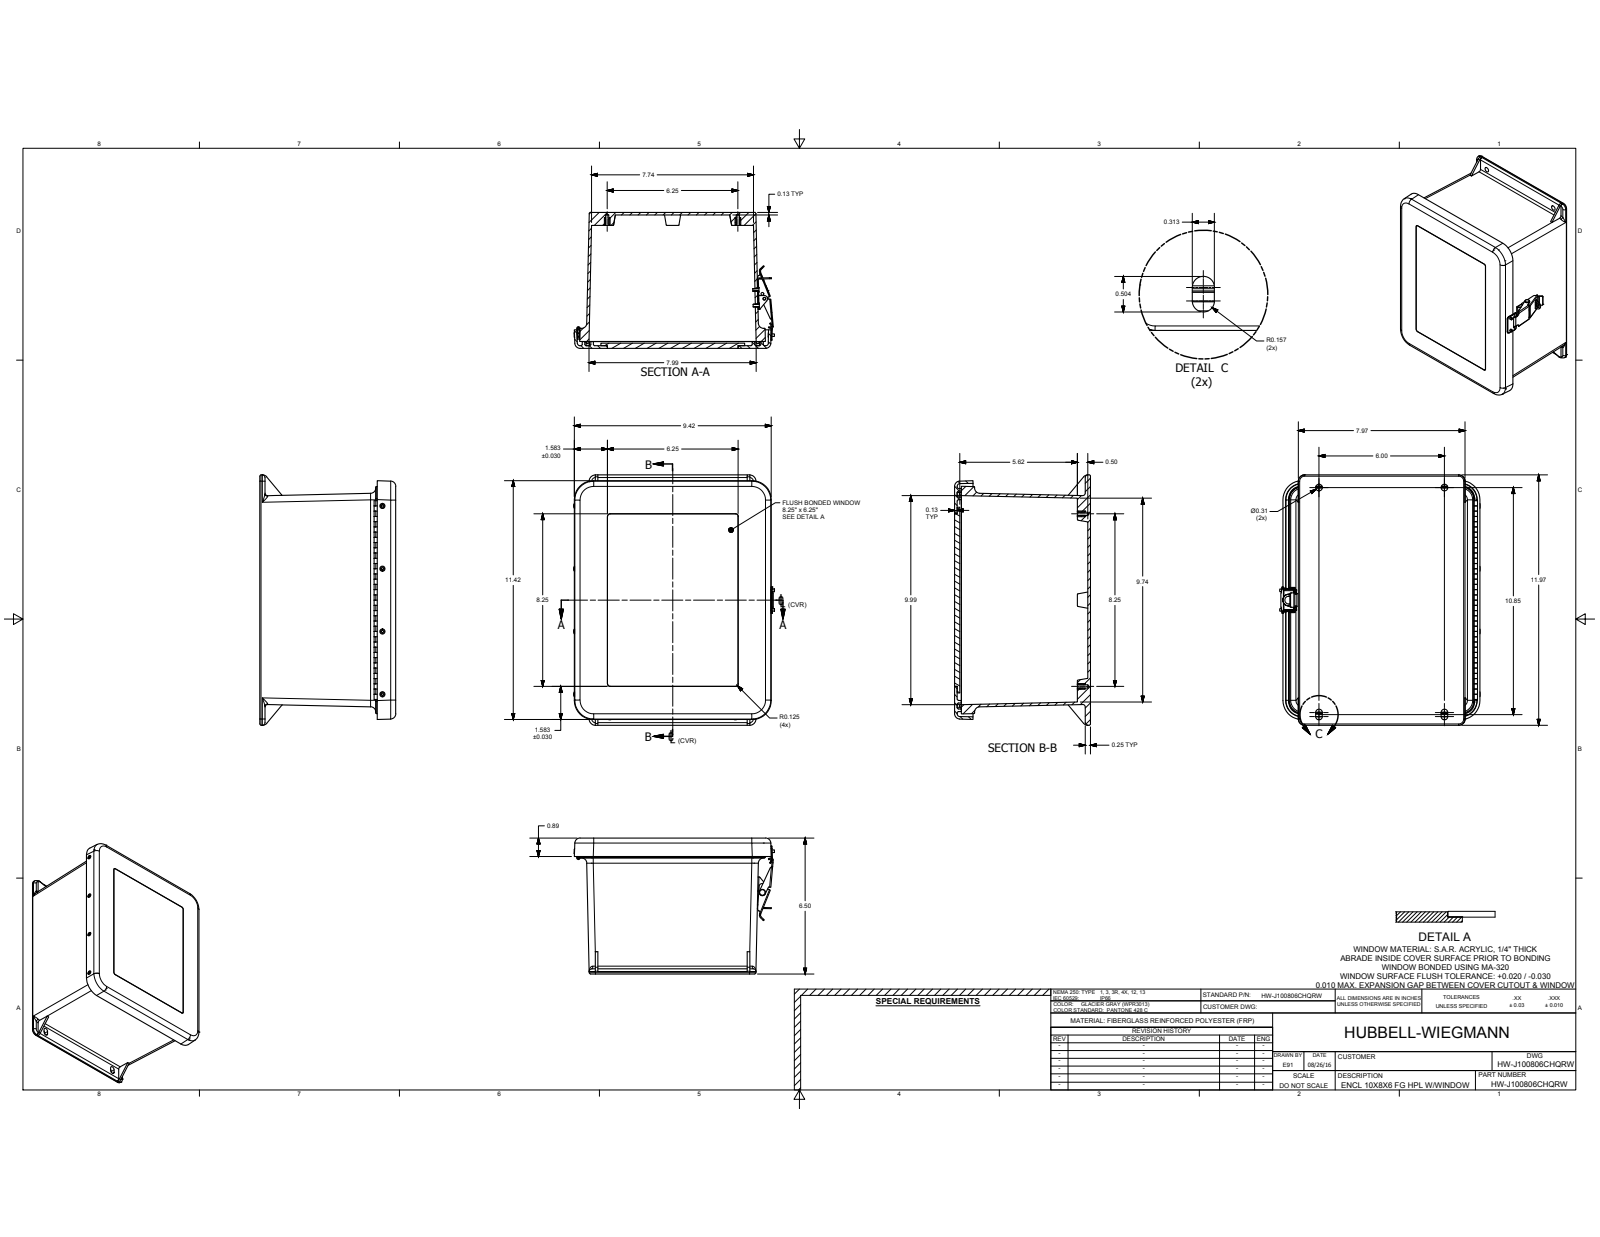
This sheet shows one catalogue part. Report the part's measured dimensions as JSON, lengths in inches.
{"part_name": "HW-J100806CHQRW; WPJ100806H&LBOX; WPJW100806HL; WPJ100806H&LCVR (+8 more)", "step_written_by": "Autodesk Inventor 2017 (CONFIG_CONTROL_DESIGN)", "units": "inches", "bodies": {"solids": 37, "faces": 1199, "planar": 465, "cylindrical": 466, "other": 268}, "overall_size": [11.966, 9.637, 6.499], "volume_in3": 84.15, "surface_area_in2": 1059, "round_holes": [[0.14, 14], [0.104, 12], [0.152, 12], [0.159, 12], [0.131, 8], [0.375, 5], [0.13, 2], [0.135, 2], [0.313, 2], [0.085, 1]], "round_bosses_or_shafts": [[0.27, 12], [0.125, 12], [0.3, 1], [0.17, 1], [0.155, 1], [0.12, 1]], "partial_cylinders_radius": [[0.063, 33], [0.031, 26], [0.125, 26], [0.063, 20], [0.039, 16], [0.015, 12], [0.3, 12], [0.25, 10]], "face_to_face_distances": [6.249, 0.125, 6.499, 0.122, 0.123, 0.25, 6.374, 6.124, 0.125, 6.374], "hole_center_spacings": [6, 3, 2.5, 0.938, 3.5, 8.5, 9, 0.75]}
